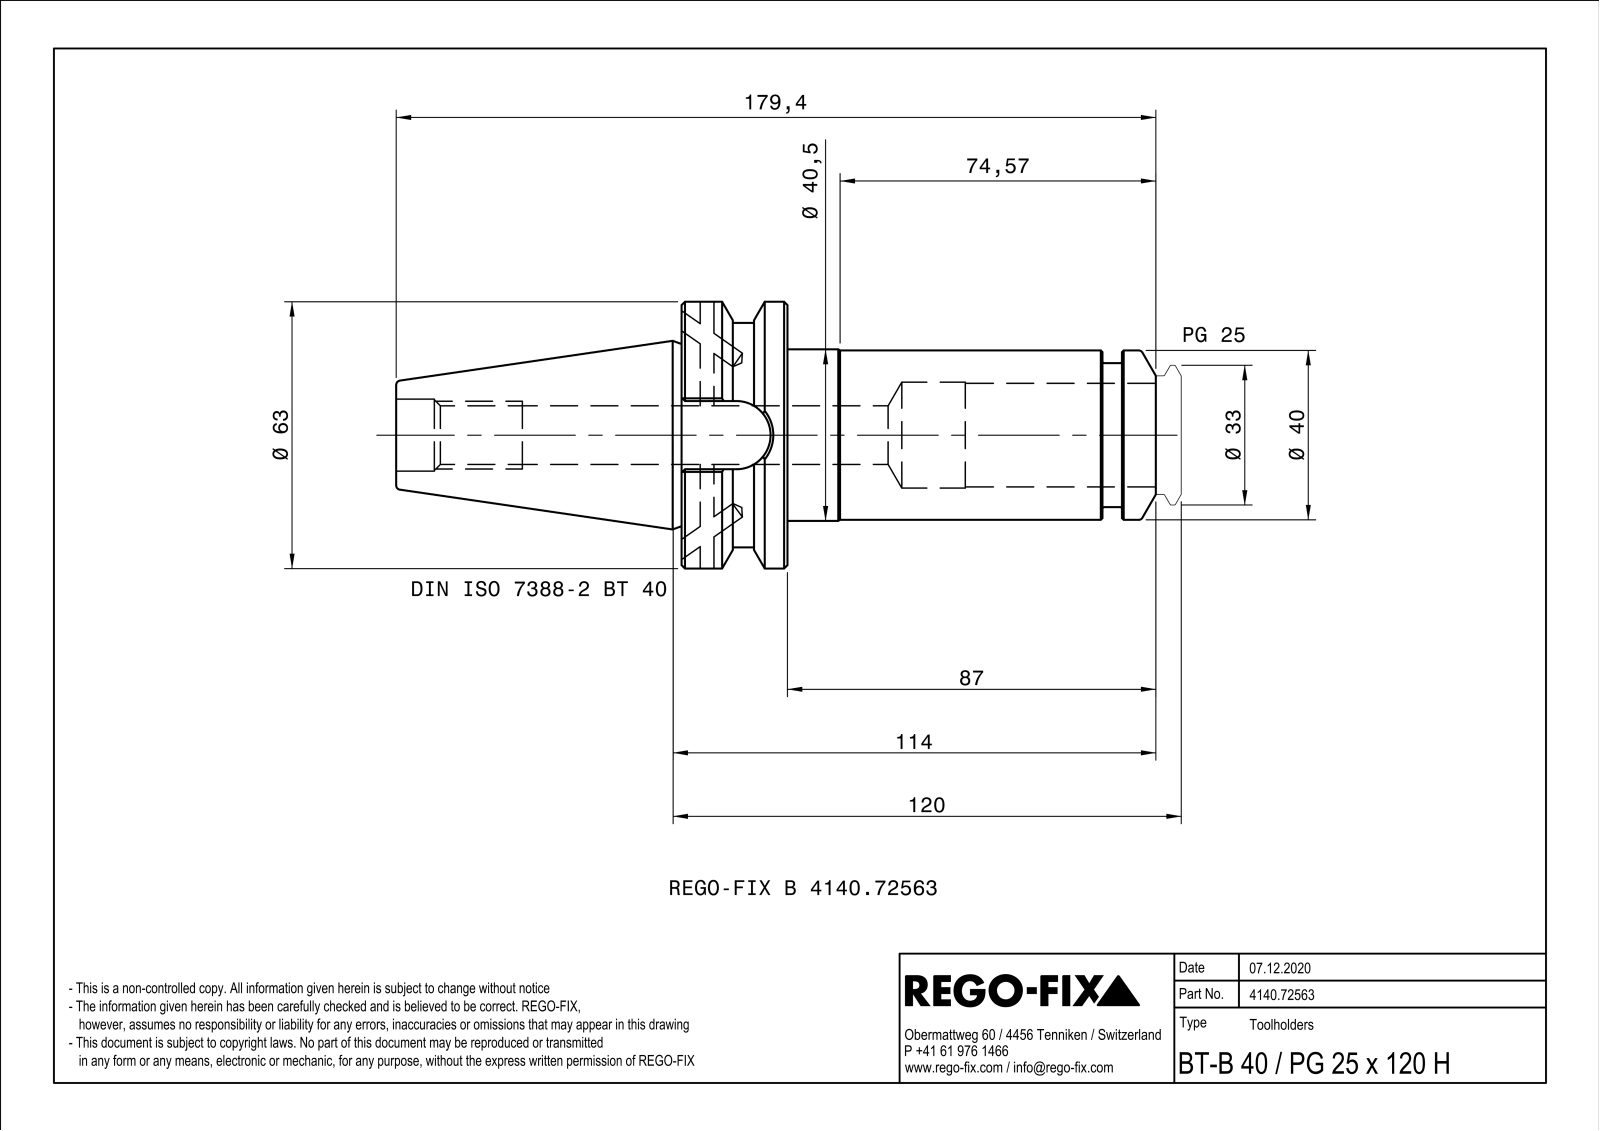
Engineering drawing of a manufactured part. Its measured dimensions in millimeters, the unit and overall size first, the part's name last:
Units: millimetres
Overall size (bounding box): 179.4 × 63 × 63
Round holes (diameter × count): ⌀3.24 ×2, ⌀3.9 ×2, ⌀13.84 ×1, ⌀17.4 ×1, ⌀25 ×1
Round bosses / shafts (diameter × count): ⌀63 ×1, ⌀53 ×1, ⌀40.5 ×1, ⌀40 ×1, ⌀34 ×1
Partial cylindrical surfaces — rounded edges, fillets, slot ends (radius × count): R0.5 ×4, R8.05 ×1
Main face-to-face distances: 25, 45.1, 74.4, 99.4, 4.6, 79, 104, 16.1, 171.4, 166.8
Volume: 191 925 mm³ · Surface area: 39 919 mm²
Bodies: 1 solid, 105 faces (32 planar, 30 cylindrical, 43 other)
Part name (STEP PRODUCT): NOCUT
STEP written by: SIEMENS PLM Software Solid Edge ST10 (AUTOMOTIVE_DESIGN)
